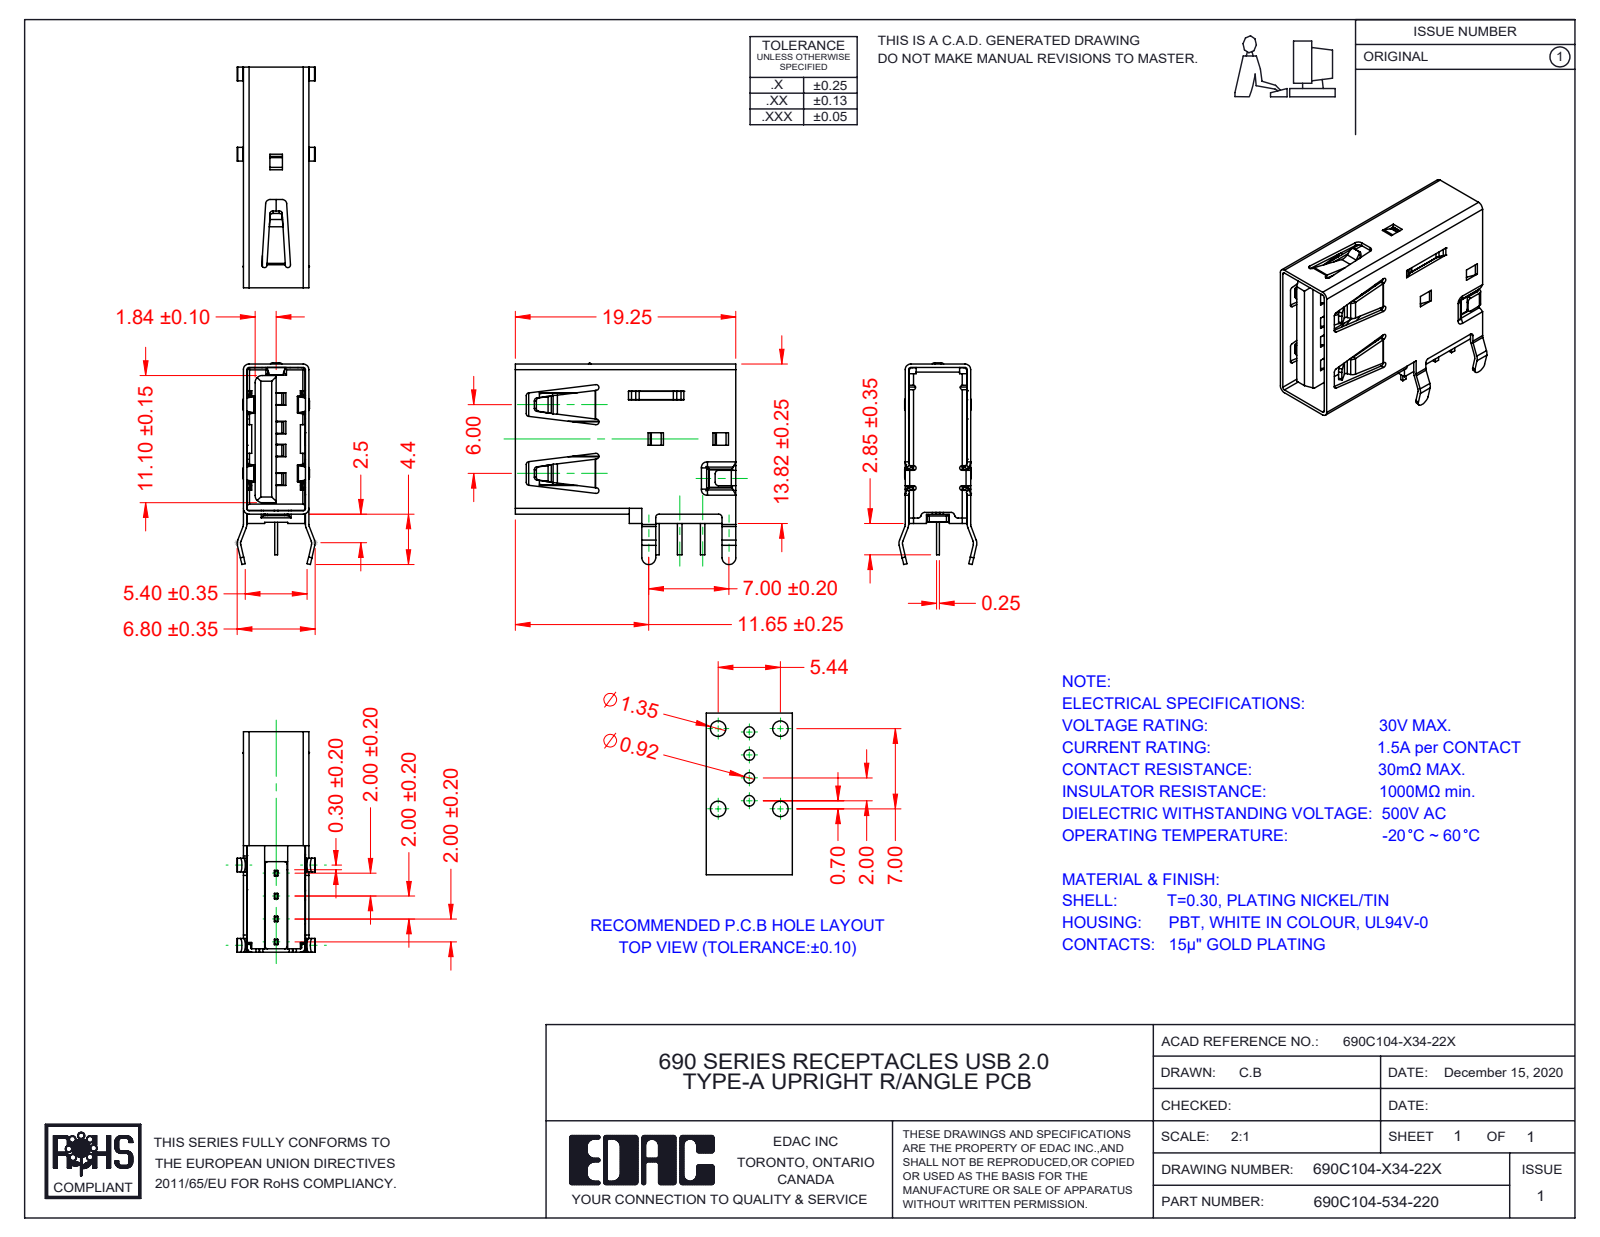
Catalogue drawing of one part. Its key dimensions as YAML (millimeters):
part_name: "Contact3 690C104-X34-22X; 690C104-134-220; Back Shell 690C104-X34-22X; Shell 690C104-X34-22X (+6 more)"
step_written_by: "SolidWorks 2020 (AUTOMOTIVE_DESIGN)"
units: millimeters
bodies: {solids: 8, faces: 1166, planar: 753, cylindrical: 317, other: 96}
overall_size: [19.25, 17.61, 6.8]
volume: 658
surface_area: 2729
partial_cylinders:
  - {radius: 0.3, count: 42}
  - {radius: 0.4, count: 24}
  - {radius: 0.6, count: 24}
  - {radius: 0.25, count: 23}
  - {radius: 0.2, count: 21}
  - {radius: 0.15, count: 18}
  - {radius: 0.1, count: 15}
  - {radius: 0.5, count: 11}
face_to_face_distances: [5.42, 5.12, 5.72, 12.8, 2.5, 2.52, 5.38, 2.86, 2.56, 4.7]
